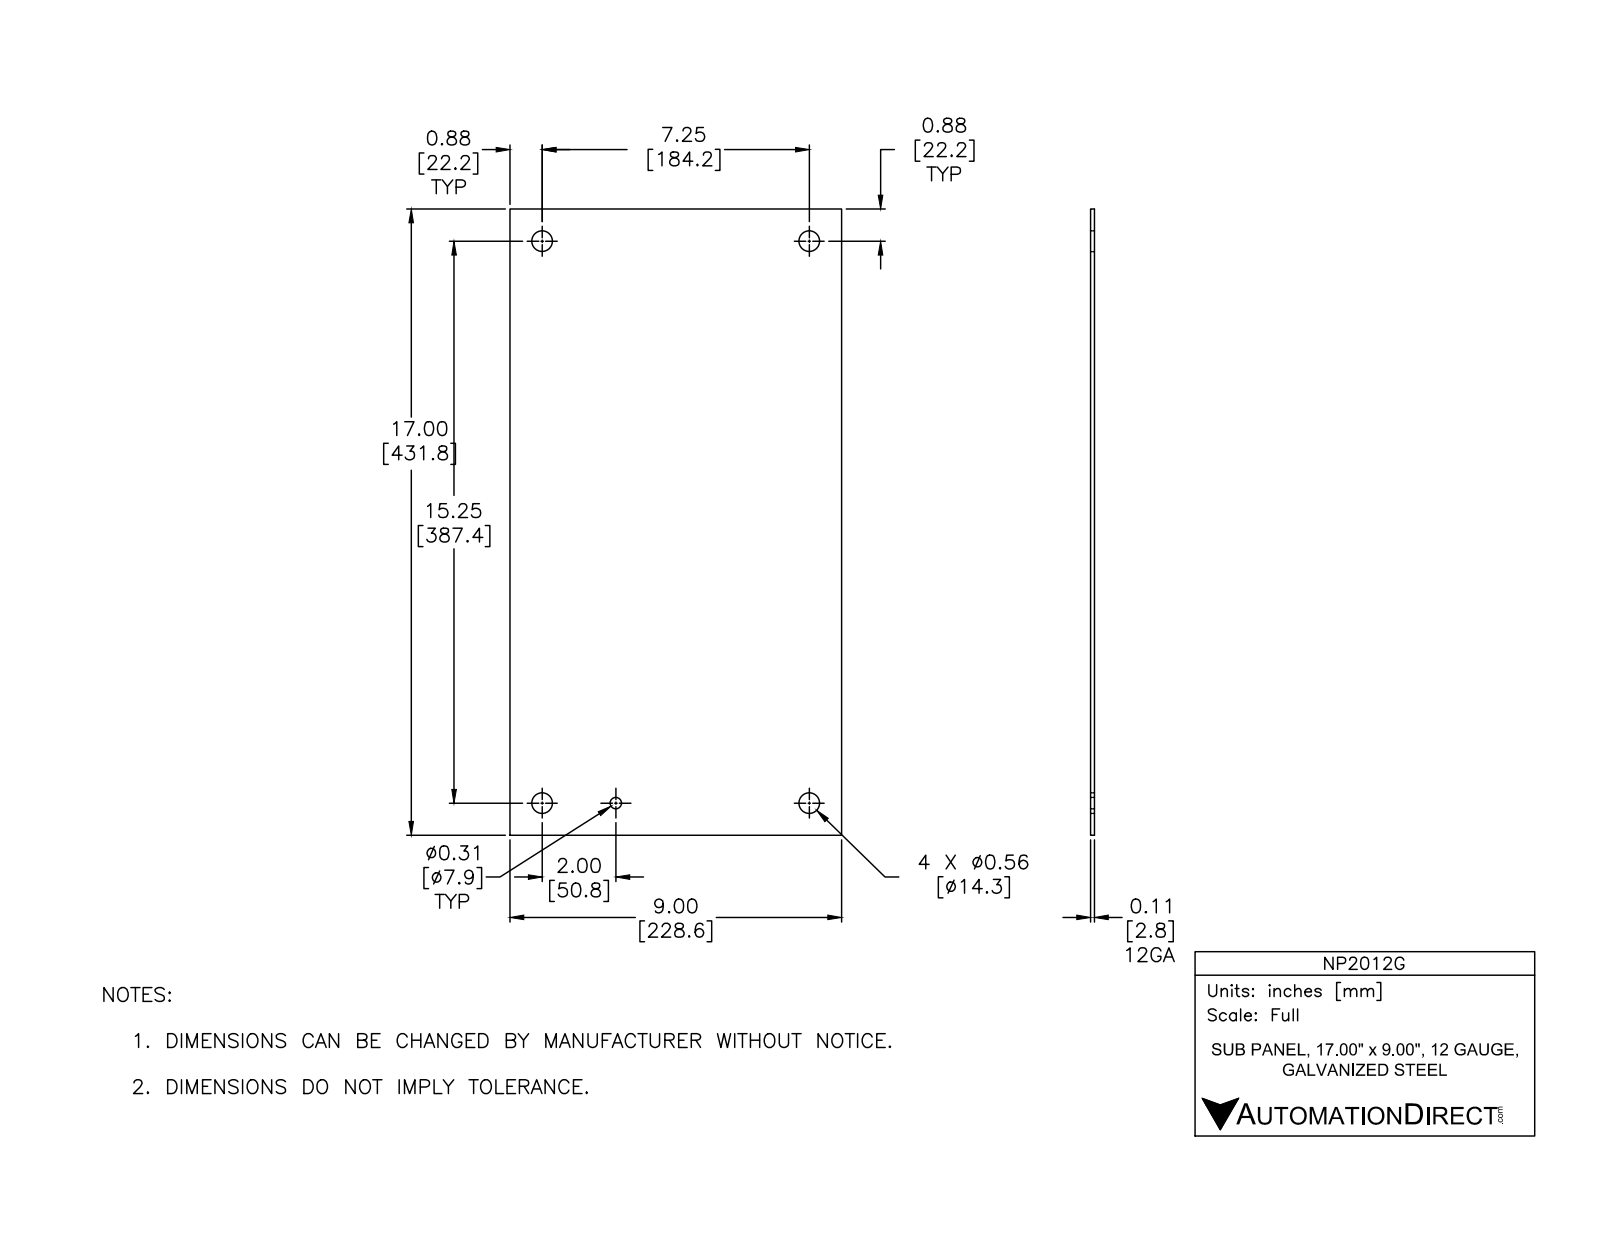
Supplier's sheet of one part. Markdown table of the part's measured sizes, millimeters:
| quantity | value |
| --- | --- |
| part name | NP2012G |
| STEP written by | Autodesk Inventor 2012 (AUTOMOTIVE_DESIGN) |
| units | millimeters |
| bodies | 1 solid, 11 faces (6 planar, 5 cylindrical, 0 other) |
| overall size | 431.8 × 228.6 × 2.4 |
| volume | 233 400 mm³ |
| surface area | 199 700 mm² |
| round holes (diameter × count) | 14.3 × 4, 7.9 × 1 |
| main face-to-face distances | 2.4, 228.6, 431.8 |
| hole center spacings | 184.2, 428.9, 50.8, 133.4, 387.4, 387.4, 390.7, 409.7 |
